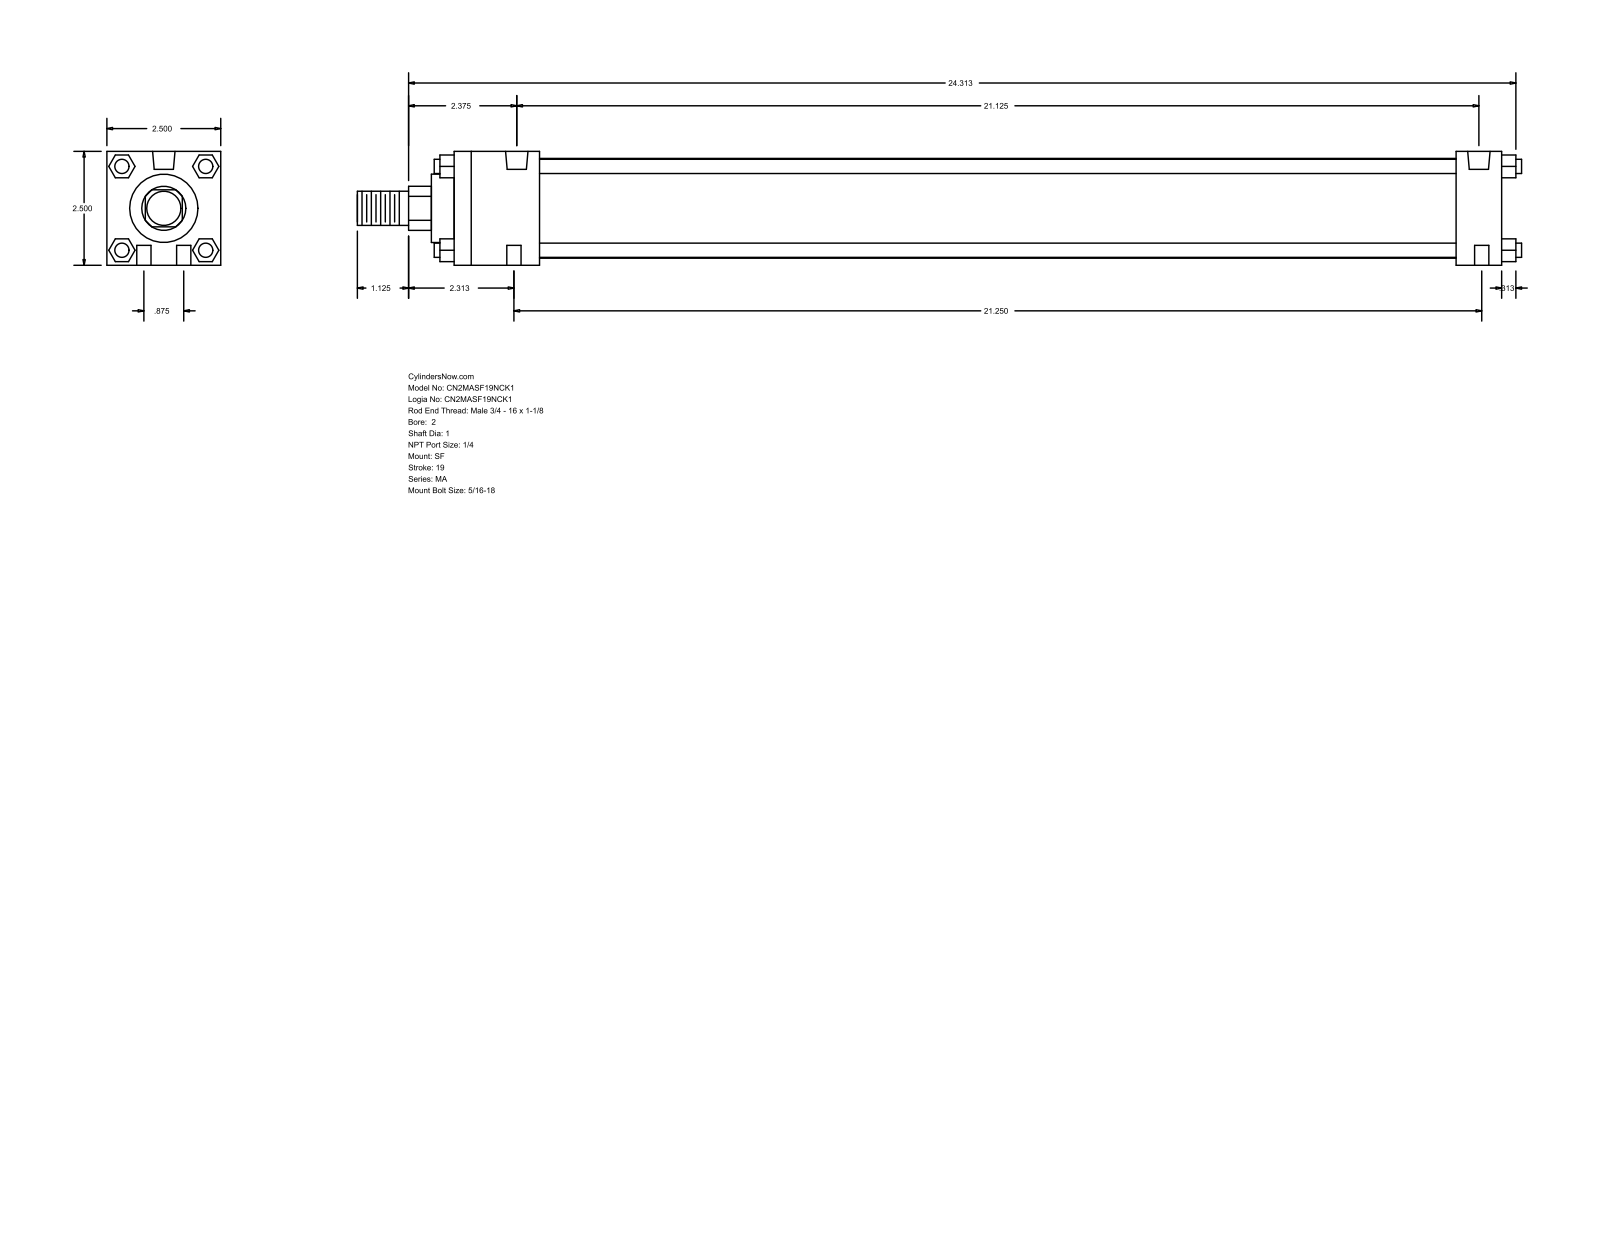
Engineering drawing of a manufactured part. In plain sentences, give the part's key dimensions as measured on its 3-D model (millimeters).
The part is named "MA_SF__0200_1". Its 3-D file was written by "GSSL Pune (CONFIG_CONTROL_DESIGN)". It is 0 solids with 124 faces: 94 planar, 30 cylindrical and 0 other. Overall it measures 649.29 by 63.5 by 63.5 millimeters. Round holes: 6 of diameter 7.94, 2 of diameter 12.49. Round bosses or shafts: 4 of diameter 7.94, 1 of diameter 55.63, 1 of diameter 38.1, 1 of diameter 25.4, 1 of diameter 19.05. Partial cylindrical surfaces (rounded edges, fillets, slot ends): 1 of radius 12.29. The main face-to-face distances are 63.5, 584.2, 12.7, 25.4, 558.8, 47.63, 511.17, 536.57, 23.37, 40.47. The hole center spacings are 11.22, 538.27, 22.22, 536.57, 539.75, 540.21.
